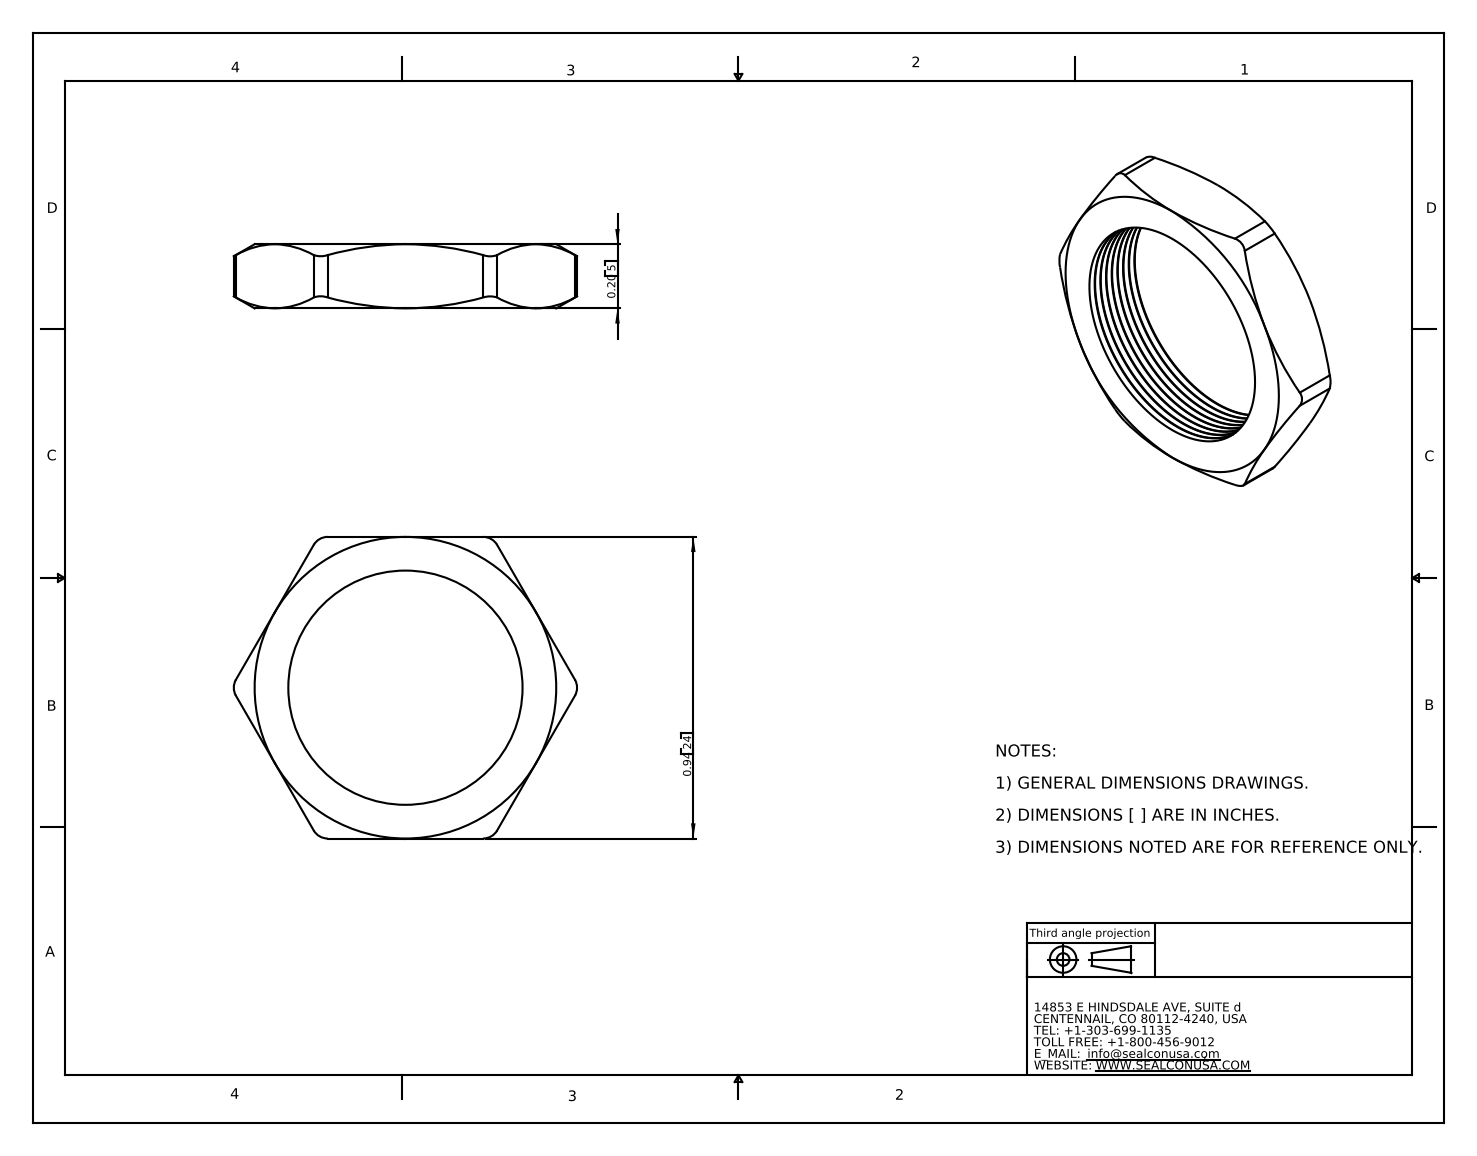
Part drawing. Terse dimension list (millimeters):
name: NP-11-GY
written by: SolidWorks 2007 (CONFIG_CONTROL_DESIGN)
unit: mm
bodies: 1 solid, 77 faces (8 planar, 23 cylindrical, 46 other)
size: 27.2 × 23.9 × 5.1
volume: 1 000 mm³; area: 1 403 mm²
holes: 1× ⌀18.5
rounds: 6× R1.3
face distances: 5.1, 23.9
